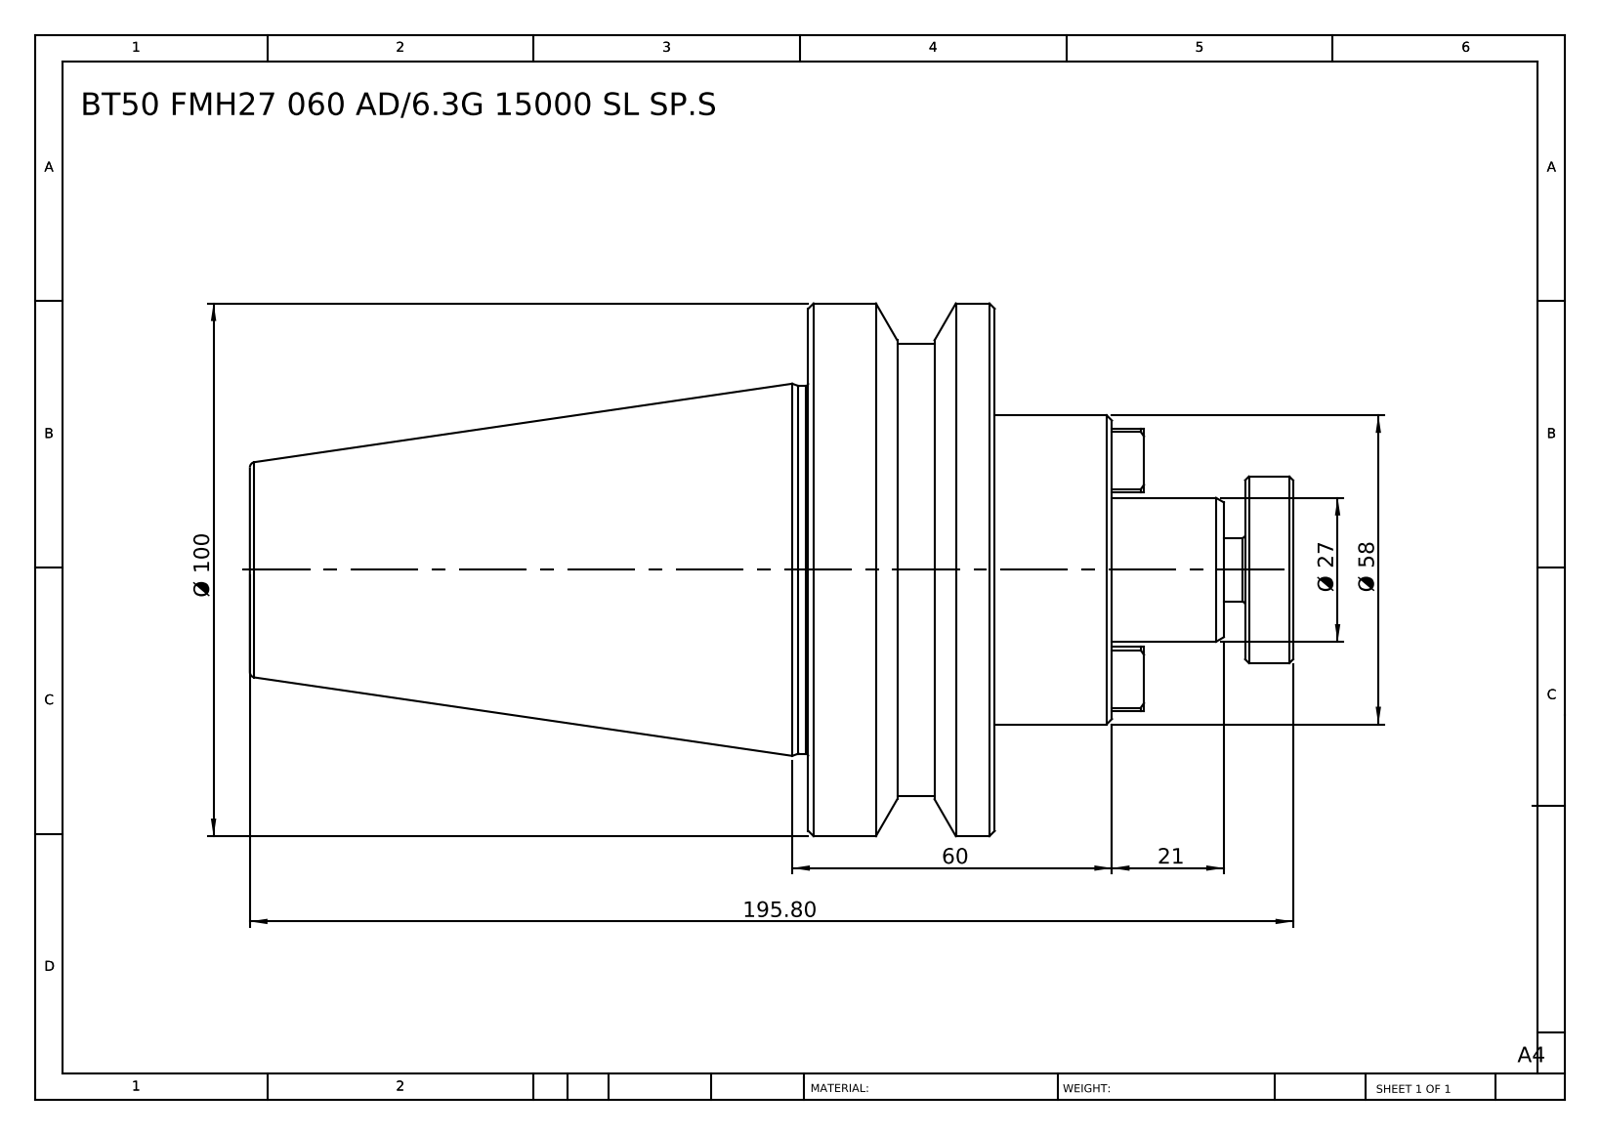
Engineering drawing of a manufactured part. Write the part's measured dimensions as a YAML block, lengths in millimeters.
part_name: "BT50 FMH27 060 AD-6.3G 15000 SL SP.S"
step_written_by: "SolidWorks 2014 (CONFIG_CONTROL_DESIGN)"
units: millimeters
bodies: {solids: 1, faces: 77, planar: 35, cylindrical: 16, other: 26}
overall_size: [195.8, 100, 100]
volume: 590878
surface_area: 53286
round_bosses_or_shafts:
  - {diameter: 100, count: 1}
  - {diameter: 85, count: 1}
  - {diameter: 69, count: 1}
  - {diameter: 58, count: 1}
  - {diameter: 35, count: 1}
  - {diameter: 27, count: 1}
  - {diameter: 12, count: 1}
face_to_face_distances: [35, 22, 57, 161.8, 139.8, 104.8, 34, 56, 91, 195.8]
